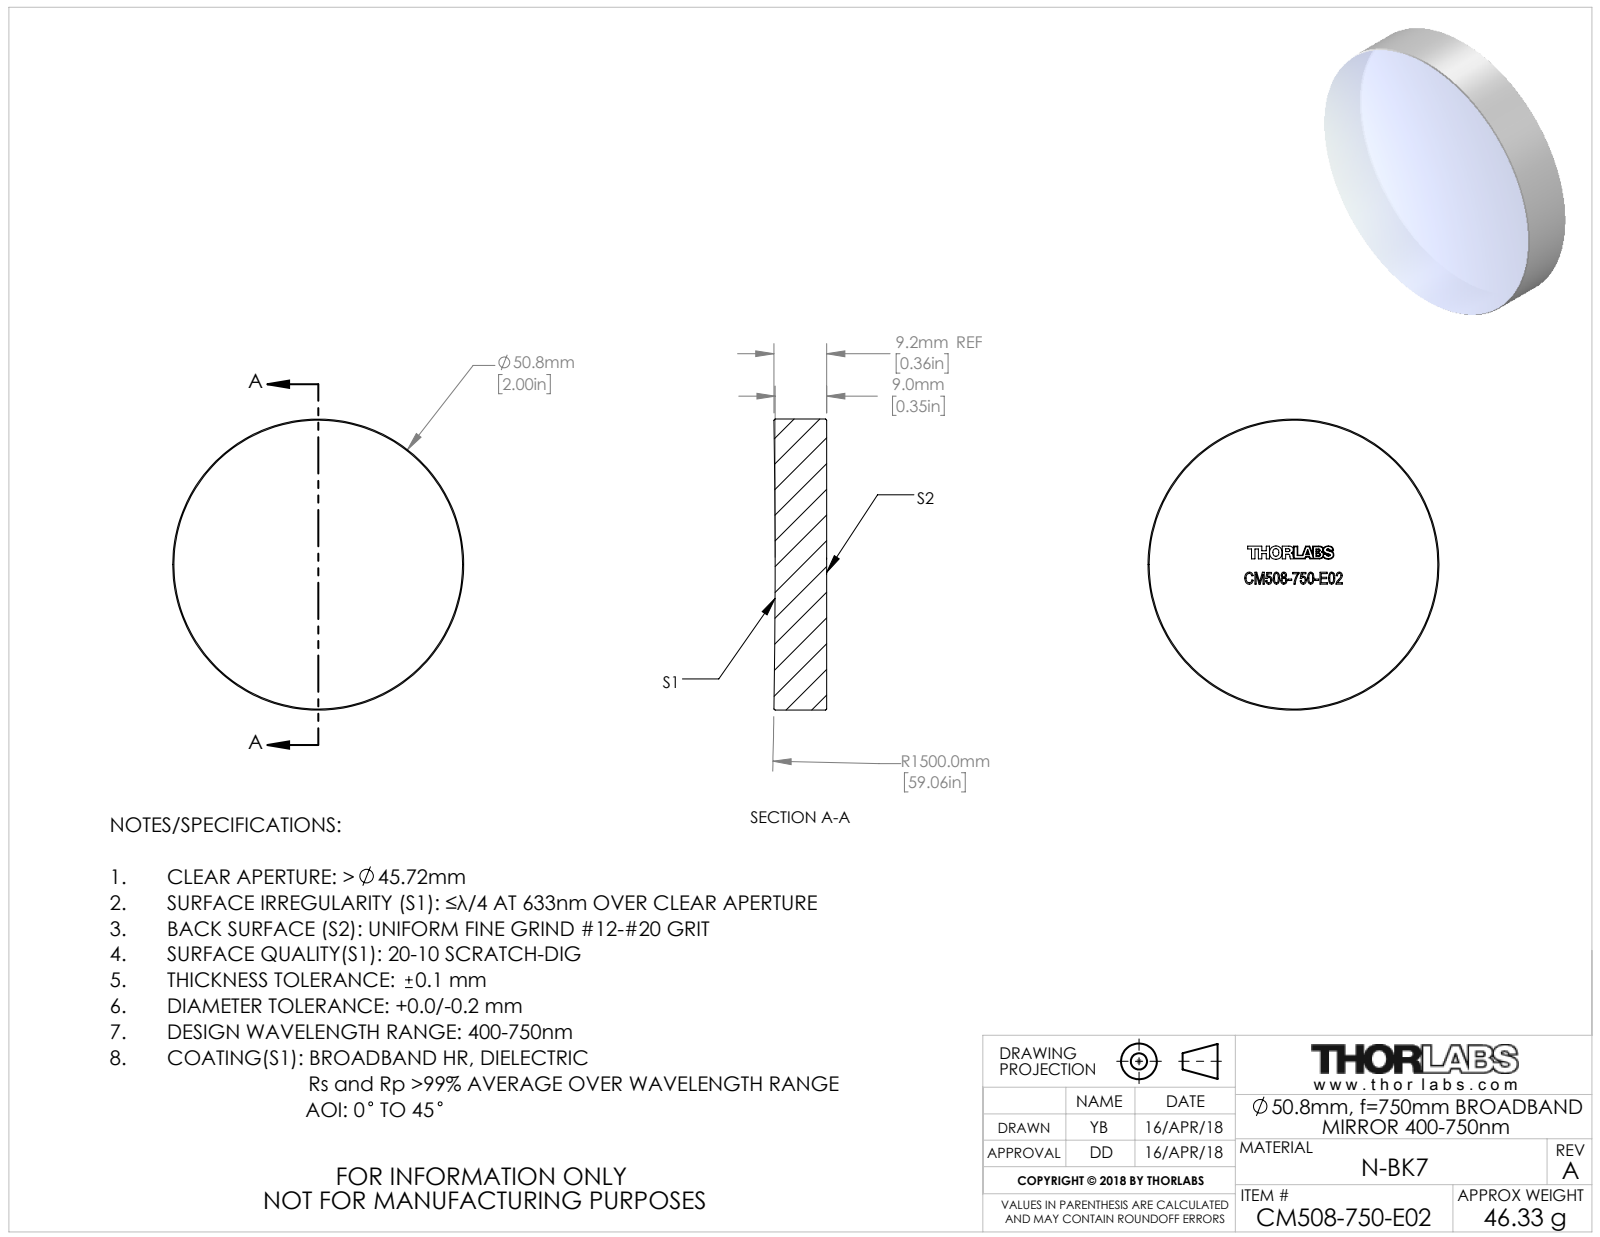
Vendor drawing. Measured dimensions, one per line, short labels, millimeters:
name: TTN153333-E0W
written by: SolidWorks 2018 (CONFIG_CONTROL_DESIGN)
unit: mm
bodies: 1 solid, 42 faces (34 planar, 2 cylindrical, 6 other)
size: 50.8 × 50.8 × 9.21
volume: 18 453 mm³; area: 5 487 mm²
bosses: 1× ⌀50.8
